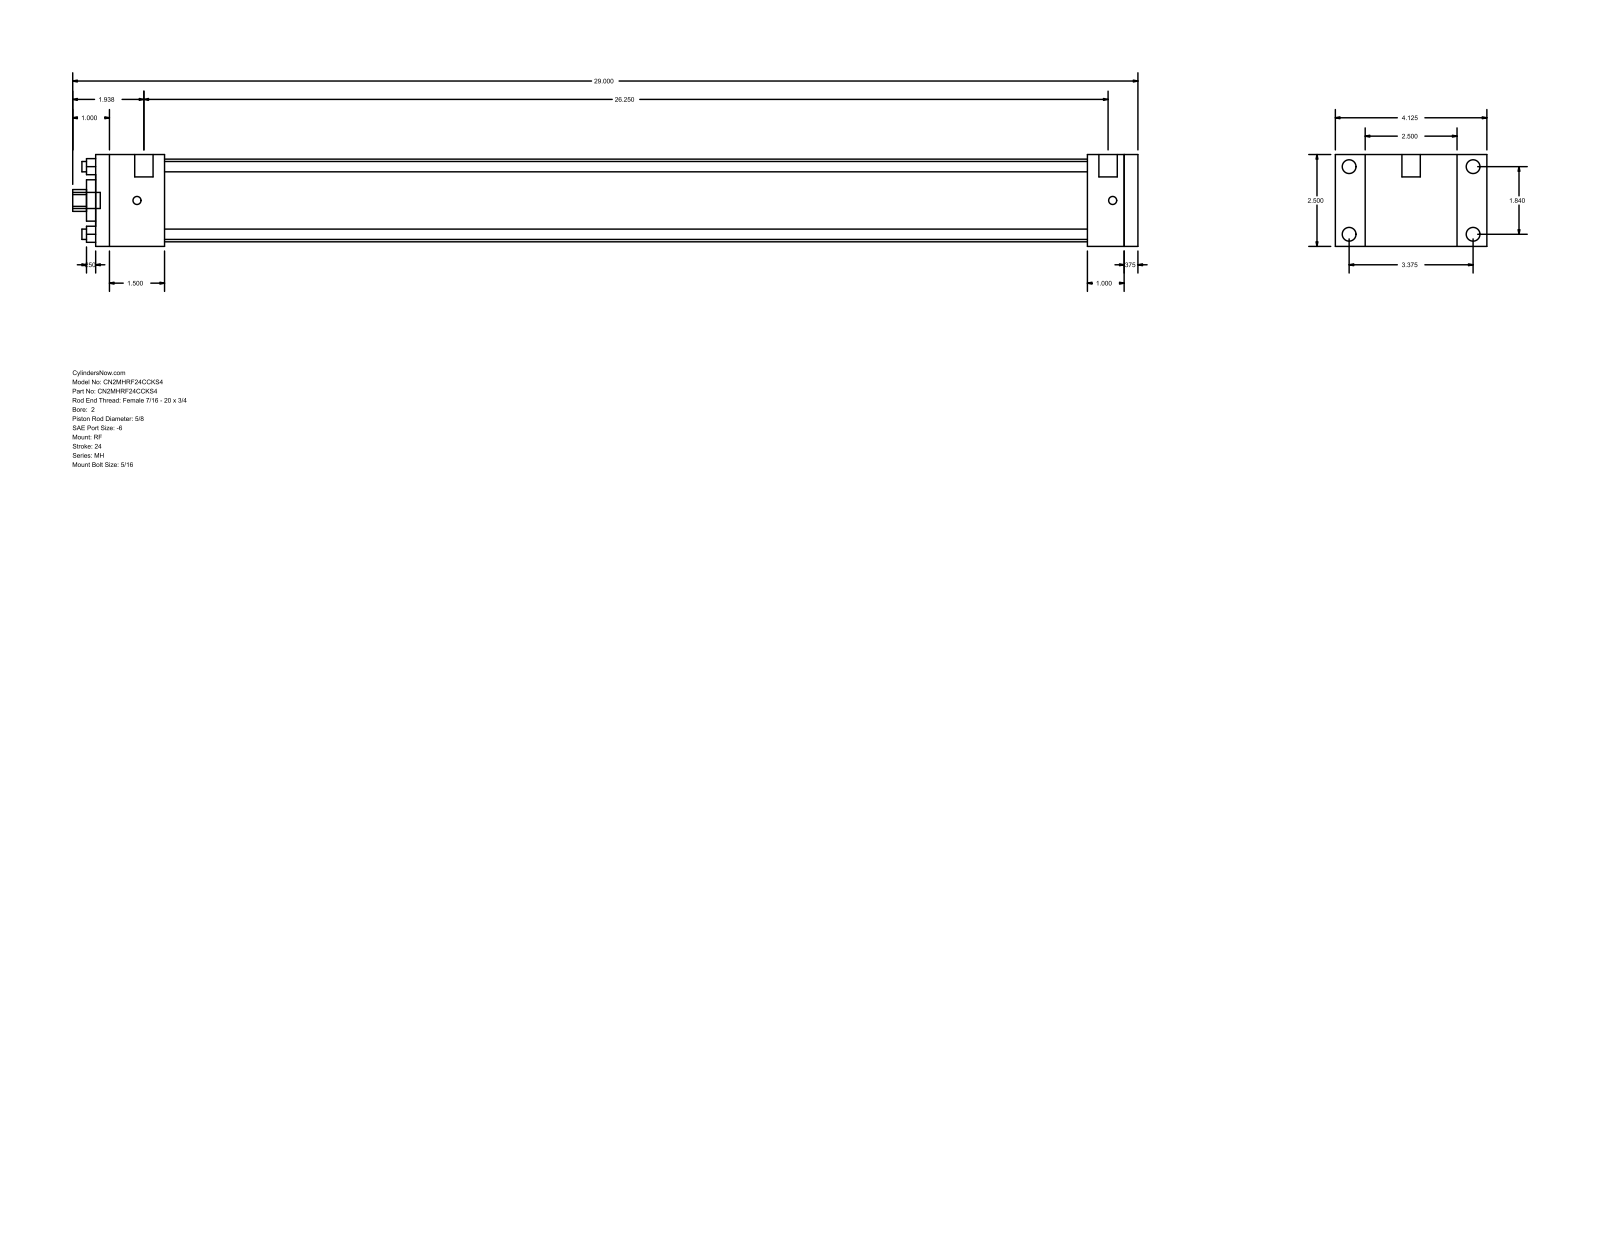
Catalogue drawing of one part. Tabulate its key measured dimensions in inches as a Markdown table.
| quantity | value |
| --- | --- |
| part name | MH_RF__0200_0.625 |
| STEP written by | GSSL Pune (CONFIG_CONTROL_DESIGN) |
| units | inches |
| bodies | 0 solids, 92 faces (64 planar, 28 cylindrical, 0 other) |
| overall size | 29 × 4.125 × 2.5 |
| round holes (diameter × count) | 0.281 × 4, 0.625 × 1, 1.125 × 1, 2.25 × 1 |
| round bosses / shafts (diameter × count) | 0.375 × 4, 0.219 × 4, 0.5 × 2, 0.437 × 1 |
| partial cylindrical surfaces (radius × count) | 0.297 × 1 |
| main face-to-face distances | 2.5, 28.375, 0.375, 28, 1.875, 27, 25.125, 26.125, 26.5, 1 |
| hole center spacings | 1.301, 1.84, 2.602 |
